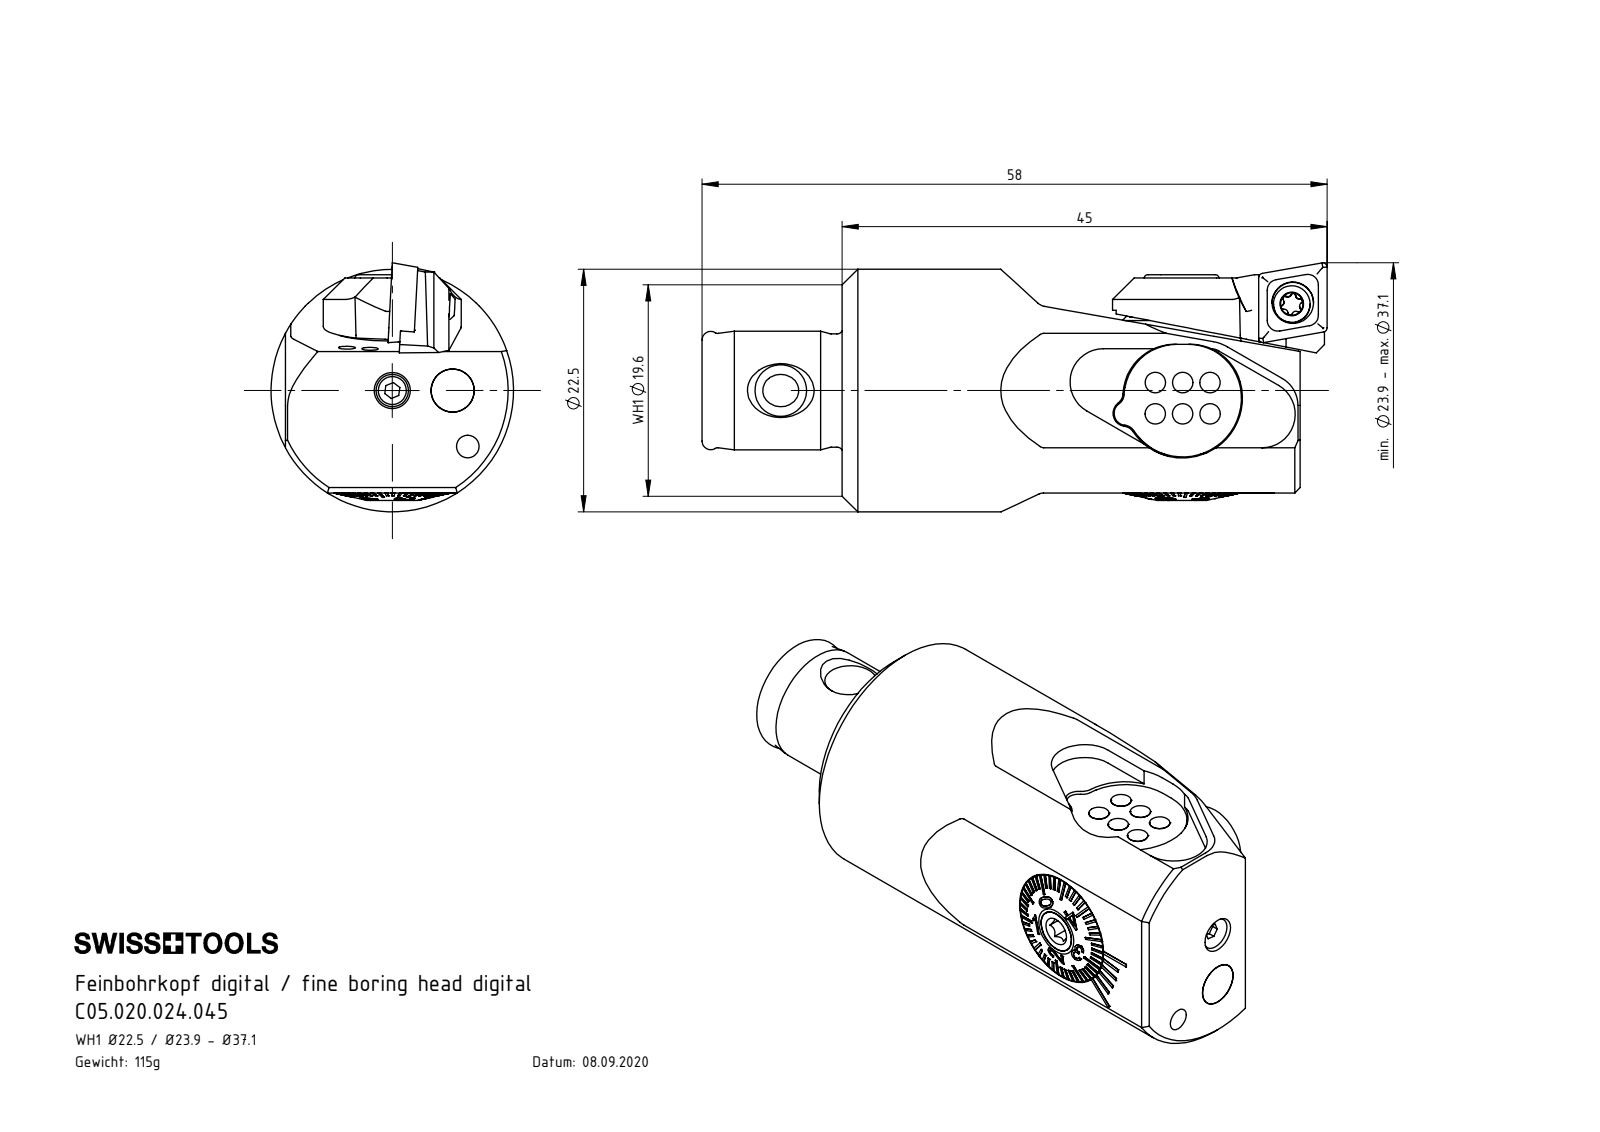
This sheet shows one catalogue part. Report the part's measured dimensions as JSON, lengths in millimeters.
{"part_name": "C05.020.024.045; F20-BG3.004.017_A; F20-BG1.DA2.011_Aktuell 06.2014-M1x2; F20-BG2.011.004_A (+8 more)", "step_written_by": "SolidWorks 2015 (AUTOMOTIVE_DESIGN)", "units": "millimeters", "bodies": {"solids": 18, "faces": 884, "planar": 386, "cylindrical": 191, "other": 307}, "overall_size": [58, 21.85, 20], "volume_mm3": 12671, "surface_area_mm2": 8838, "round_holes": [[2, 5], [3.3, 2], [4, 2], [0.7, 1], [1.6, 1], [1.9, 1], [2.05, 1], [2.2, 1], [2.4, 1], [2.5, 1], [2.8, 1], [3, 1]], "round_bosses_or_shafts": [[1.9, 6], [6, 2], [4, 2], [3.95, 2], [20, 1], [11, 1], [10.98, 1], [10.85, 1]], "partial_cylinders_radius": [[0.21, 6], [0.36, 5], [1.1, 3], [1.2, 3], [5, 3], [0.3, 2], [0.5, 2], [2, 2]], "face_to_face_distances": [42.5, 15.05, 1.5, 2.8, 3.7, 1.4, 11.35, 0.8, 1.45, 14.25], "hole_center_spacings": [1.14, 2.6, 3.51, 4.44, 5.6, 8.3, 22.75]}
